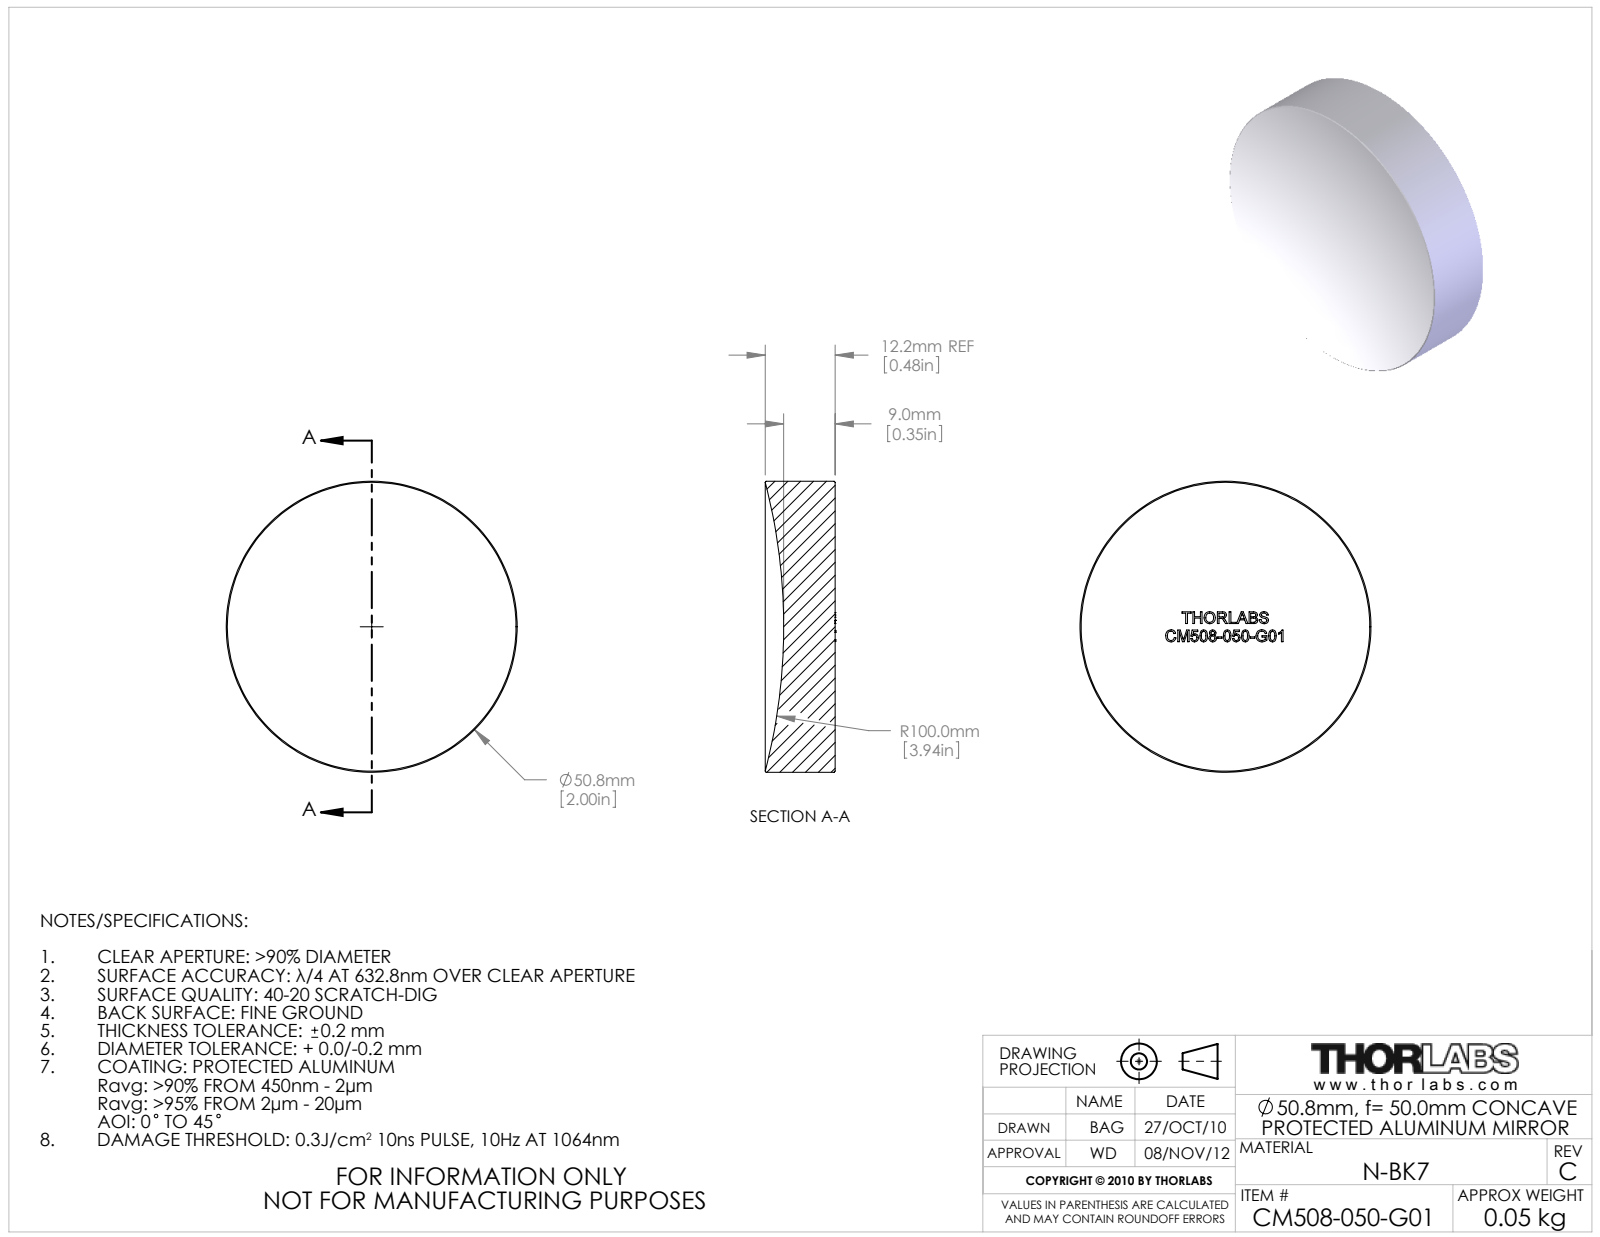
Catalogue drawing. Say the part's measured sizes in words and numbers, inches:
The part is named "12013-E0W". Its 3-D file was written by "SolidWorks 2009 (AUTOMOTIVE_DESIGN)". It is 1 solid with 285 faces: 140 planar, 2 cylindrical and 143 other. Overall it measures 2 by 2 by 0.481 inches. Its volume is 1.314 cubic inches and its surface area 9.306 square inches. Round bosses or shafts: 1 of diameter 2. The main face-to-face distances are 0.218, 0.038, 0.081, 0.206, 0.055, 0.116, 0.101, 0.117, 0.081, 0.249.
